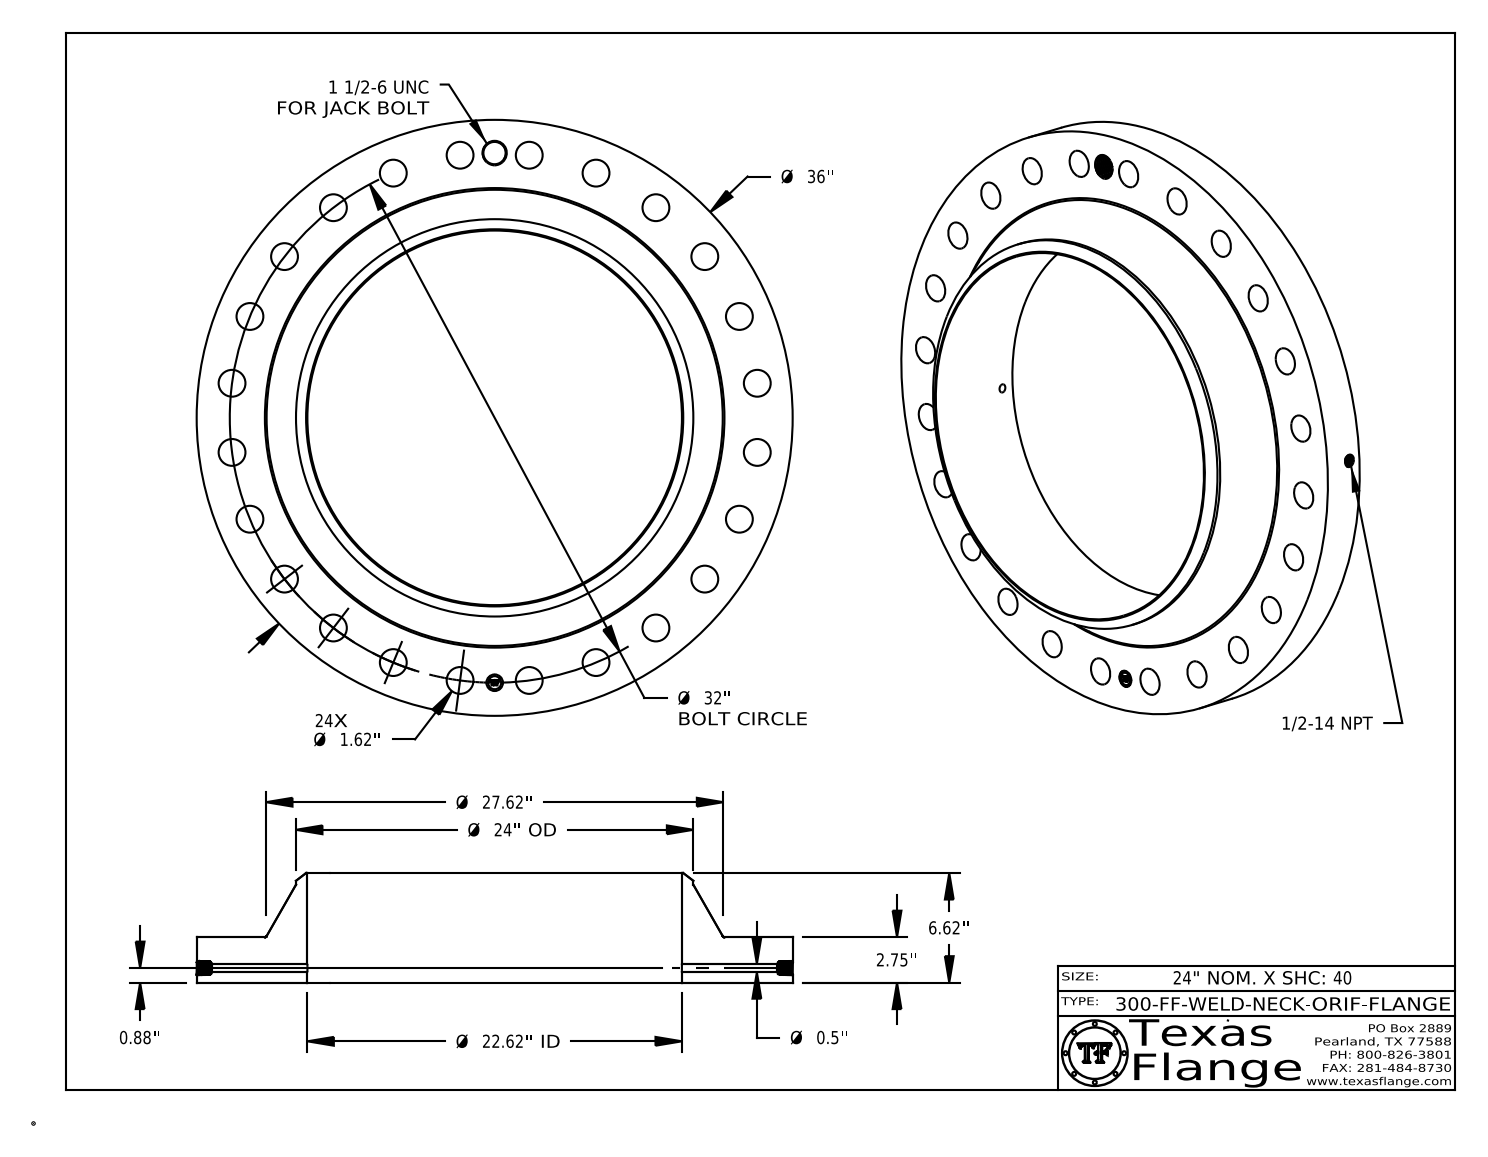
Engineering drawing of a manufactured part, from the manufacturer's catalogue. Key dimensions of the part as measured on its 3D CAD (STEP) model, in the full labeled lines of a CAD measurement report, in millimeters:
Part name (STEP PRODUCT): 300-FF-WELD-NECK
STEP written by: CATIA V5 STEP AP214 (AUTOMOTIVE_DESIGN)
Units: millimetres
Bodies: 1 solid, 807 faces (368 planar, 127 cylindrical, 312 other)
Overall size (bounding box): 914.4 × 914.4 × 168.1
Volume: 32 150 000 mm³ · Surface area: 1 591 000 mm²
Round holes (diameter × count): ⌀41.1 ×24, ⌀12.7 ×1, ⌀17.1 ×1, ⌀25.4 ×1, ⌀34.1 ×1, ⌀574.6 ×1
Round bosses / shafts (diameter × count): ⌀1.5 ×8, ⌀914.4 ×1, ⌀609.6 ×1, ⌀20 ×1
Main face-to-face distances: 69.9, 168.1, 98.3, 69.5, 0.4, 98.7, 7.6, 7.4, 1.4, 6.3
Hole centre spacings: 406.4, 703.9, 785.1, 106.1, 494.8, 805.8, 210.4, 311
